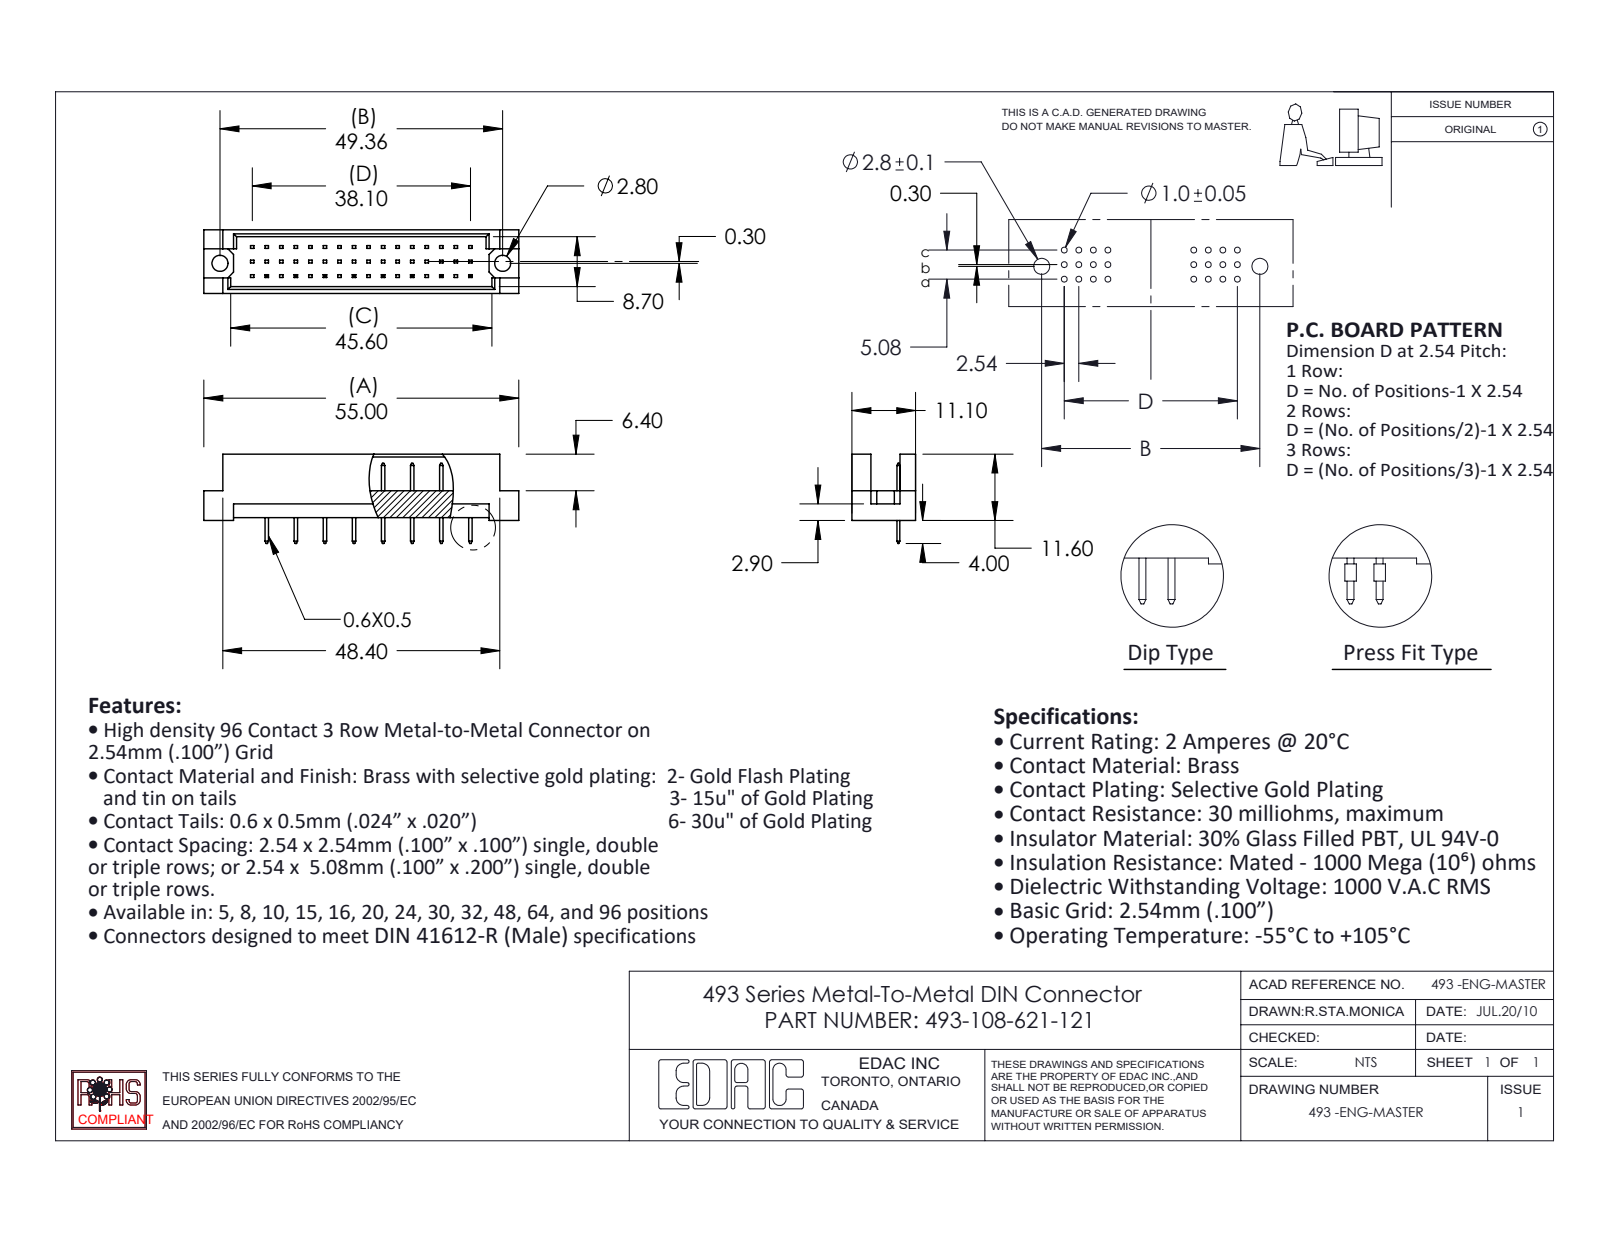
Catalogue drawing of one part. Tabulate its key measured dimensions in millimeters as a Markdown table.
| quantity | value |
| --- | --- |
| part name | 493-290_21; 493-108-621-122; 493 Part_48 |
| STEP written by | SolidWorks 2020 (CONFIG_CONTROL_DESIGN) |
| units | millimeters |
| bodies | 9 solids, 356 faces (352 planar, 4 cylindrical, 0 other) |
| overall size | 55 × 15.6 × 11.1 |
| volume | 3 305 mm³ |
| surface area | 4 000 mm² |
| round holes (diameter × count) | 2.8 × 2 |
| main face-to-face distances | 1.2, 9.9, 11.1, 8.7, 4.7, 0.5, 5.08, 2.54, 2.76, 8.34 |
| hole center spacings | 49.36 |
